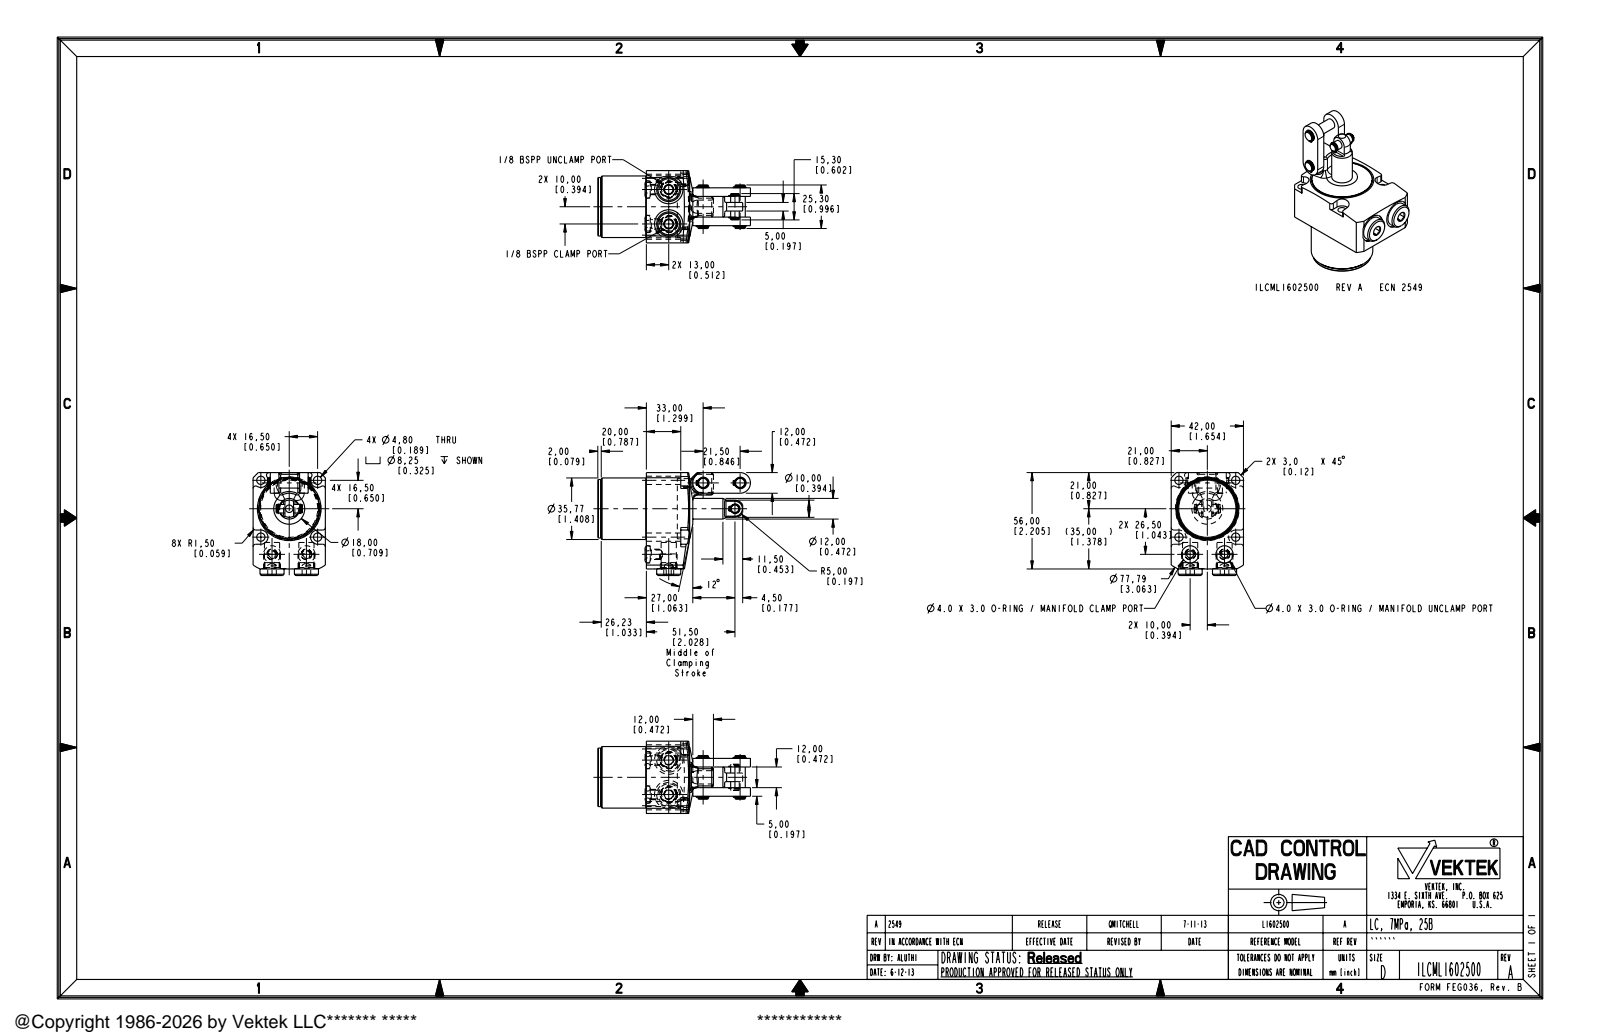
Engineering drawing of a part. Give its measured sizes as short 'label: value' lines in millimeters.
name: ILCML1602500_BODY; ILCML1602500_LUG; ILCML1602500_ASM
written by: PRO/ENGINEER BY PARAMETRIC TECHNOLOGY CORPORATION, 2007460 (AUTOMOTIVE_DESIGN_CC2)
unit: mm
bodies: 4 solids, 381 faces (139 planar, 171 cylindrical, 71 other)
size: 88.73 × 59.81 × 42
volume: 91 570 mm³; area: 24 266 mm²
holes: 6× ⌀0.66, 4× ⌀4.8, 4× ⌀5, 2× ⌀8.84, 2× ⌀10, 2× ⌀16.5, 1× ⌀35
bosses: 4× ⌀6, 2× ⌀14, 2× ⌀9.73, 2× ⌀8.25, 2× ⌀6.68, 2× ⌀5.64, 1× ⌀35.77, 1× ⌀34
rounds: 10× R1.5, 6× R0.66, 4× R1.07, 4× R4.12, 2× R0.8, 2× R1.59, 2× R6, 1× R2.79
face distances: 42, 18, 46.23, 28.23, 10, 5, 32, 27, 12, 15
hole spacings: 23.33, 28.32, 33, 1.52, 11.93, 15.22, 20, 21.5
